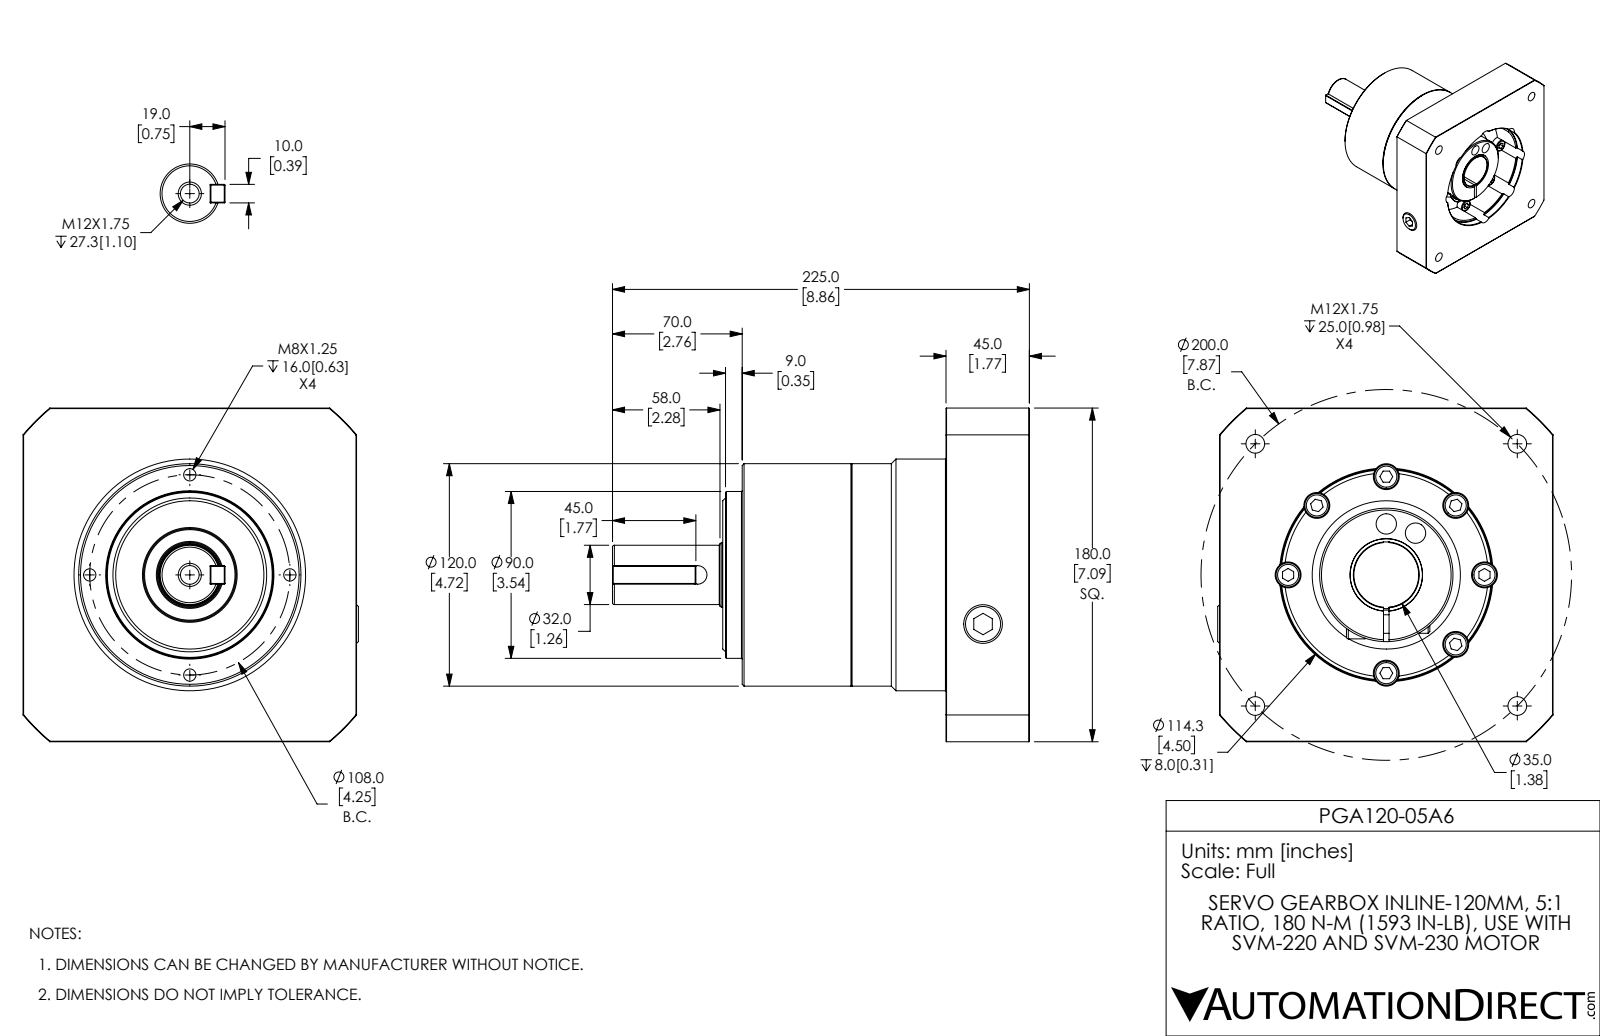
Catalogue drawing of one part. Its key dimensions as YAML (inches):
part_name: "PGA120-05A6"
step_written_by: "SolidWorks 2019 (CONFIG_CONTROL_DESIGN)"
units: inches
bodies: {solids: 1, faces: 382, planar: 149, cylindrical: 107, other: 126}
overall_size: [8.858, 7.126, 7.087]
volume: 149.2
surface_area: 301.2
round_holes:
  - {diameter: 0.551, count: 7}
  - {diameter: 0.398, count: 5}
  - {diameter: 0.262, count: 4}
  - {diameter: 0.433, count: 3}
  - {diameter: 0.689, count: 1}
  - {diameter: 1.378, count: 1}
  - {diameter: 3.15, count: 1}
round_bosses_or_shafts:
  - {diameter: 0.512, count: 7}
  - {diameter: 4.921, count: 1}
  - {diameter: 4.724, count: 1}
  - {diameter: 3.543, count: 1}
  - {diameter: 2.835, count: 1}
  - {diameter: 1.535, count: 1}
  - {diameter: 1.496, count: 1}
  - {diameter: 1.26, count: 1}
partial_cylinders:
  - {radius: 0.165, count: 1}
  - {radius: 0.197, count: 1}
  - {radius: 2.165, count: 1}
  - {radius: 2.25, count: 1}
  - {radius: 4.626, count: 1}
face_to_face_distances: [1.772, 7.087, 0.354, 4.685, 6.102, 4.331, 1.417, 0.413, 6.516, 4.744]
hole_center_spacings: [2.861, 2.87, 2.979, 5.61, 5.644, 2.087, 1.597, 1.613]
